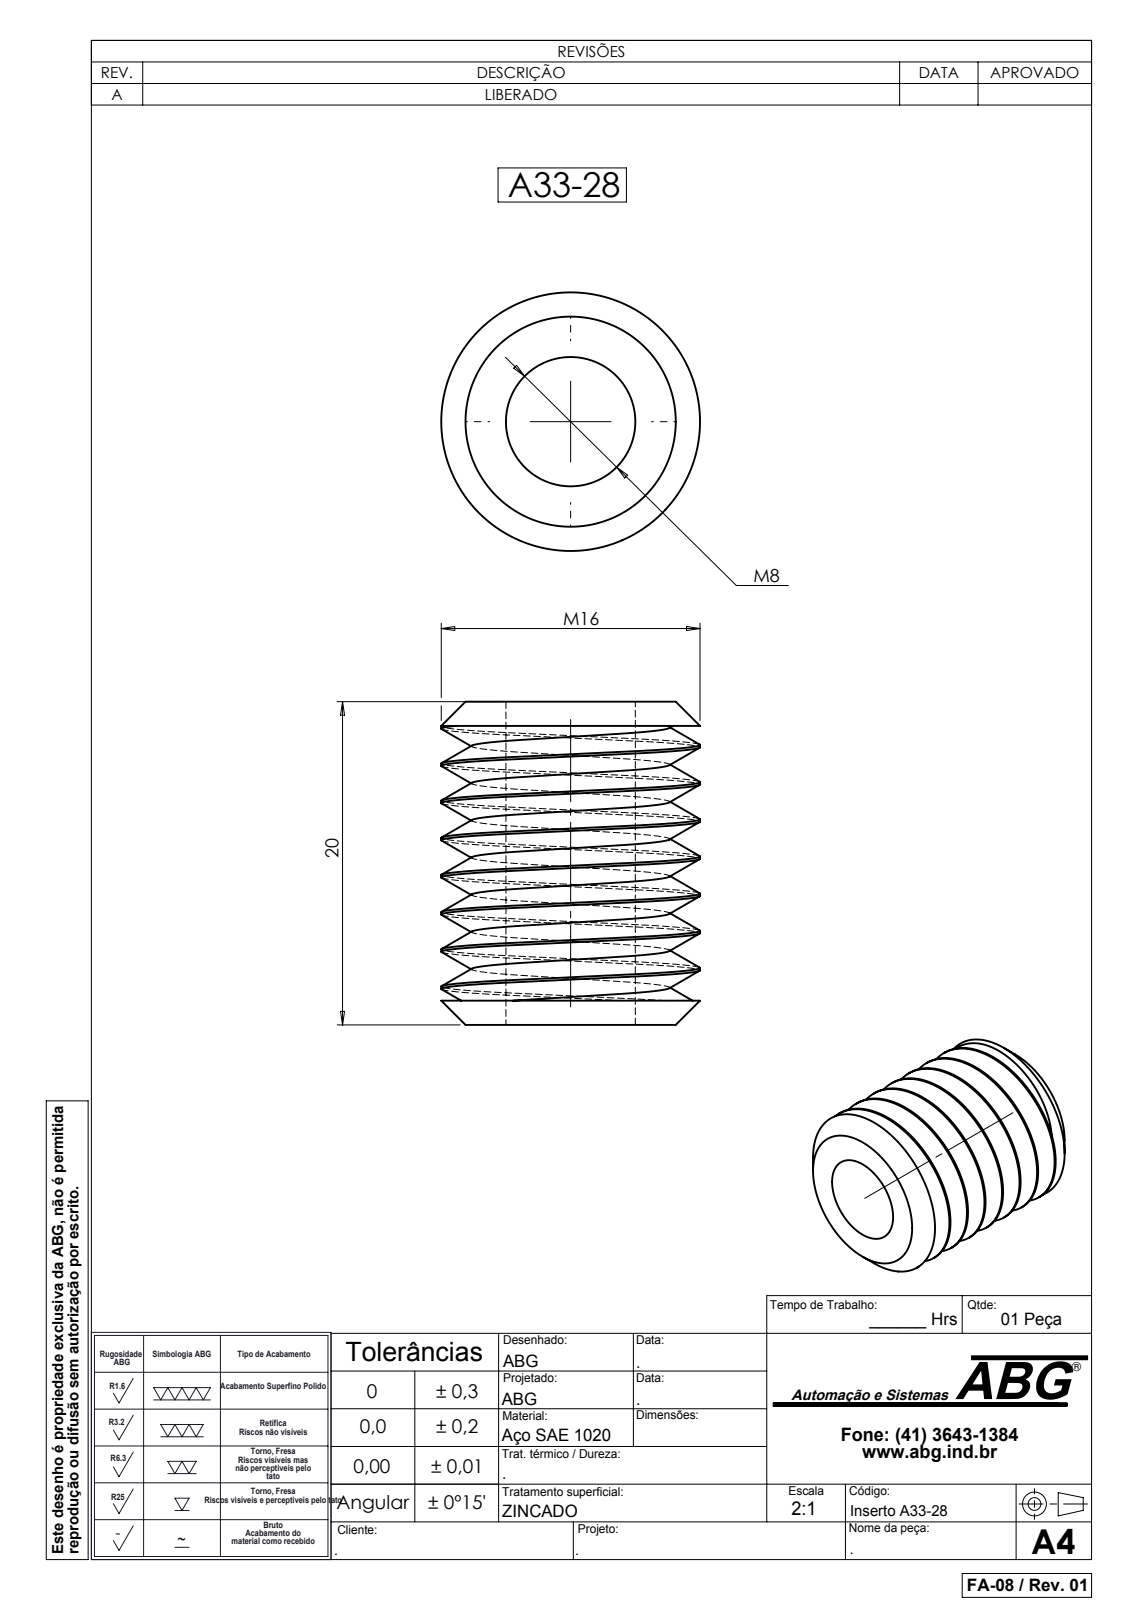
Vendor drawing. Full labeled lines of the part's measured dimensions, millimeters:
Part name (STEP PRODUCT): A33-28
STEP written by: SolidWorks 2007 (CONFIG_CONTROL_DESIGN)
Units: millimetres
Bodies: 1 solid, 28 faces (4 planar, 18 cylindrical, 6 other)
Overall size (bounding box): 20 × 16 × 16
Volume: 2 226 mm³ · Surface area: 2 413 mm²
Round holes (diameter × count): ⌀8 ×1
Round bosses / shafts (diameter × count): ⌀16 ×1
Main face-to-face distances: 20, 1.5, 18.5, 17
